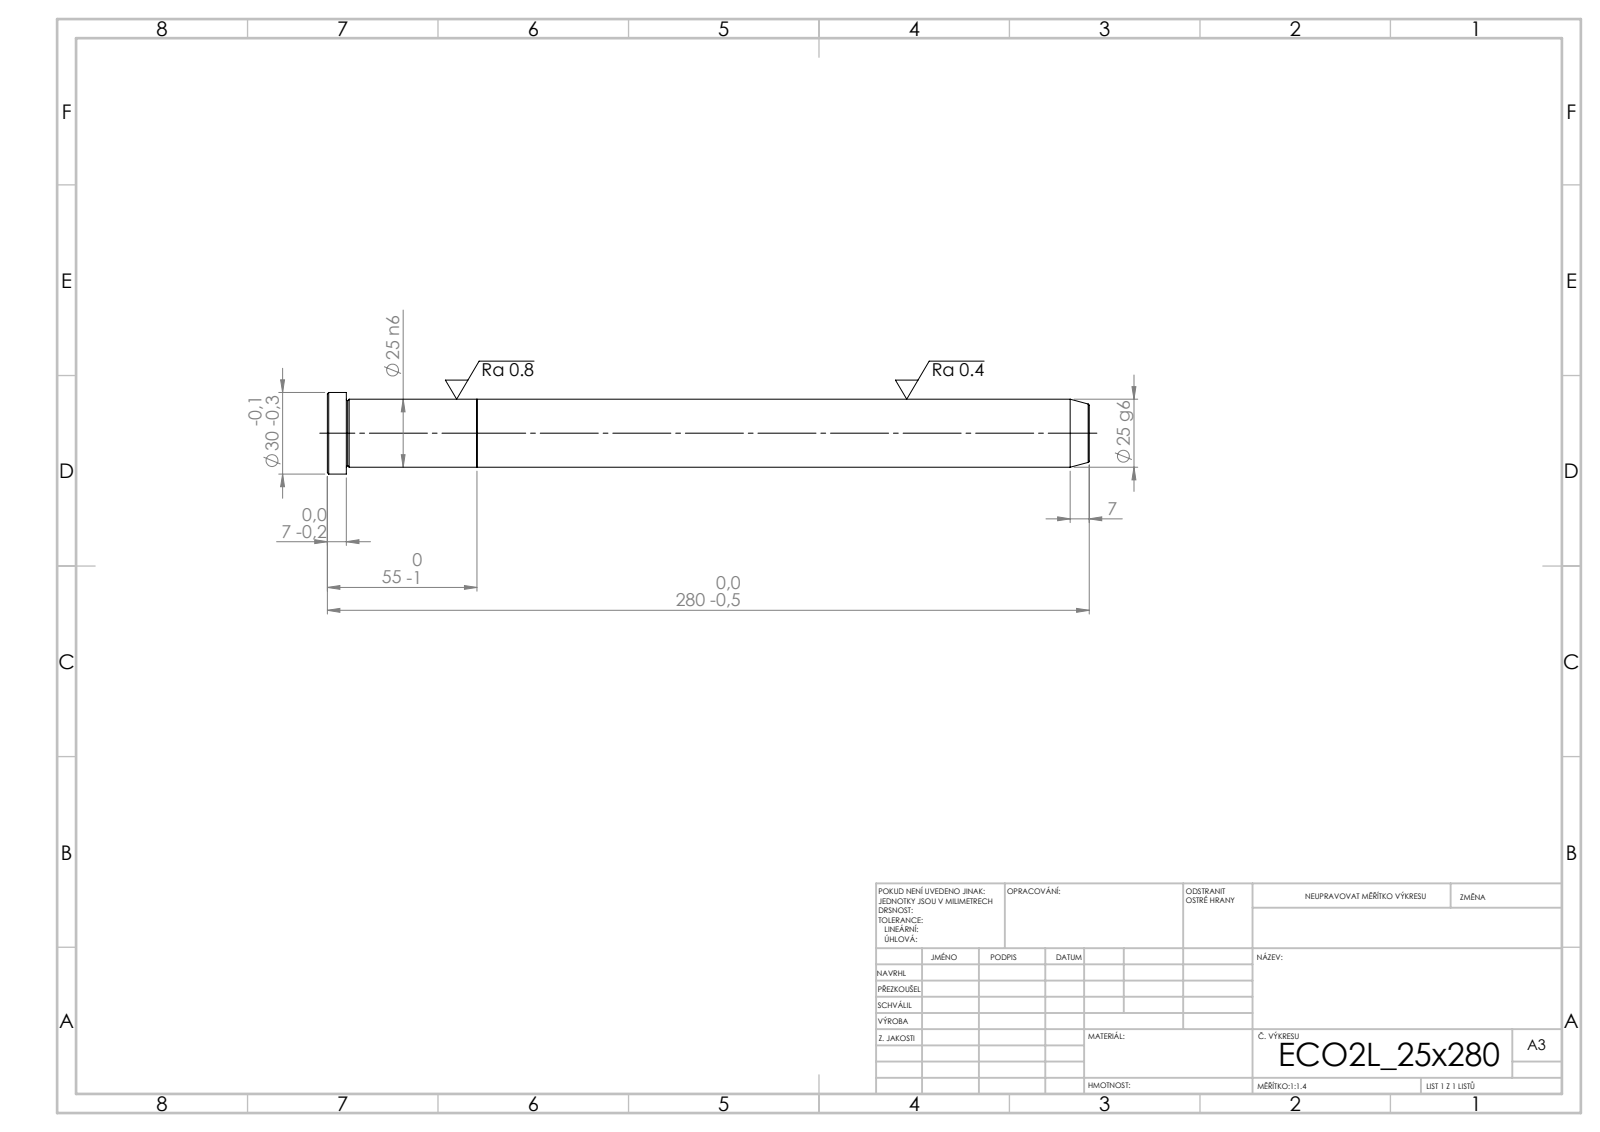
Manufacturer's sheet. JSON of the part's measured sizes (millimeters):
{"step_written_by": "SolidWorks 2019 (CONFIG_CONTROL_DESIGN)", "units": "millimeters", "bodies": {"solids": 2, "faces": 21, "planar": 5, "cylindrical": 6, "other": 10}, "overall_size": [280, 30, 30], "volume_mm3": 138423, "surface_area_mm2": 24343, "round_bosses_or_shafts": [[30, 1], [25, 1]], "face_to_face_distances": [55, 225, 280, 273, 48, 7]}
